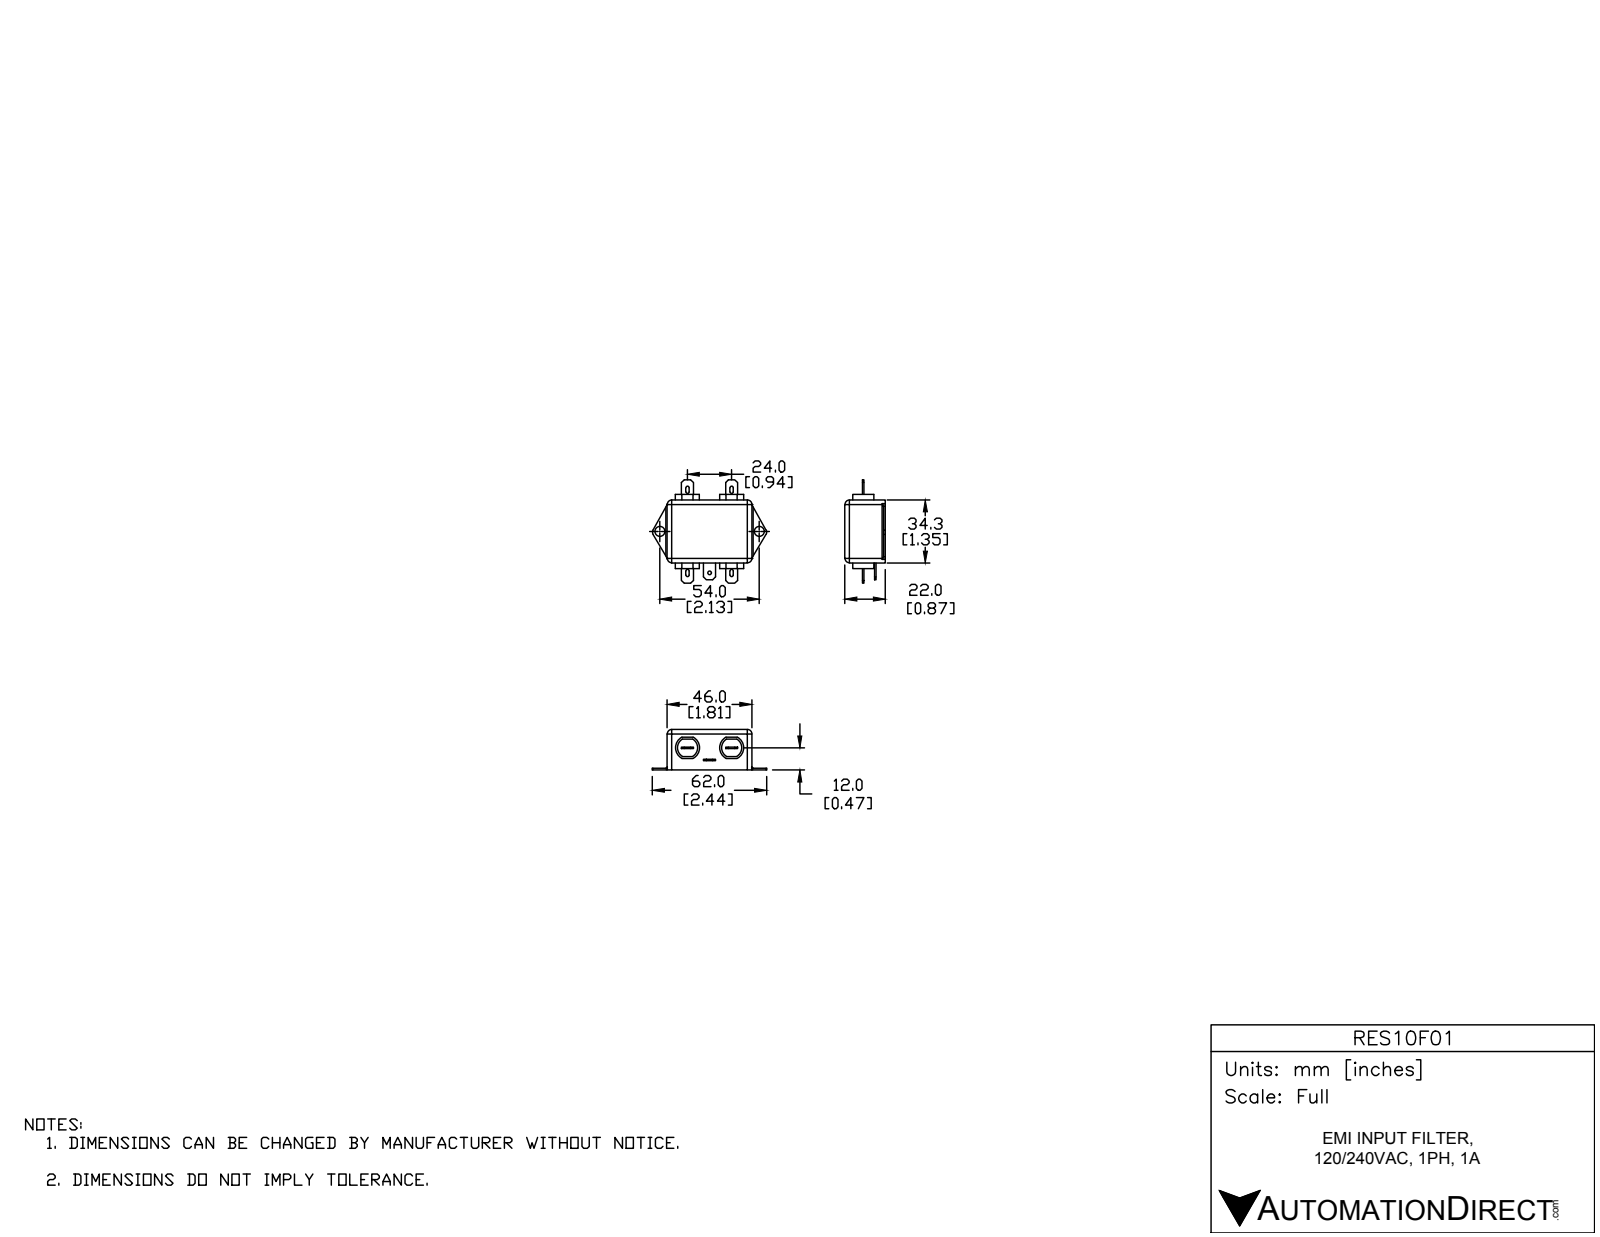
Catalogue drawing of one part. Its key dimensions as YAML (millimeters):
part_name: "RES10F01"
step_written_by: "SolidWorks 2015 (AUTOMOTIVE_DESIGN)"
units: millimeters
bodies: {solids: 1, faces: 137, planar: 79, cylindrical: 54, other: 4}
overall_size: [61.3, 56.1, 22]
volume: 35744
surface_area: 8153
round_holes:
  - {diameter: 5.3, count: 2}
  - {diameter: 2, count: 1}
partial_cylinders:
  - {radius: 2.5, count: 10}
  - {radius: 0.9, count: 8}
  - {radius: 0.75, count: 2}
  - {radius: 5.5, count: 2}
  - {radius: 6.5, count: 2}
face_to_face_distances: [22, 34.3, 46, 1.4, 35.7, 0.8, 1, 11.6, 12.4, 10.4]
hole_center_spacings: [35.11, 54]
